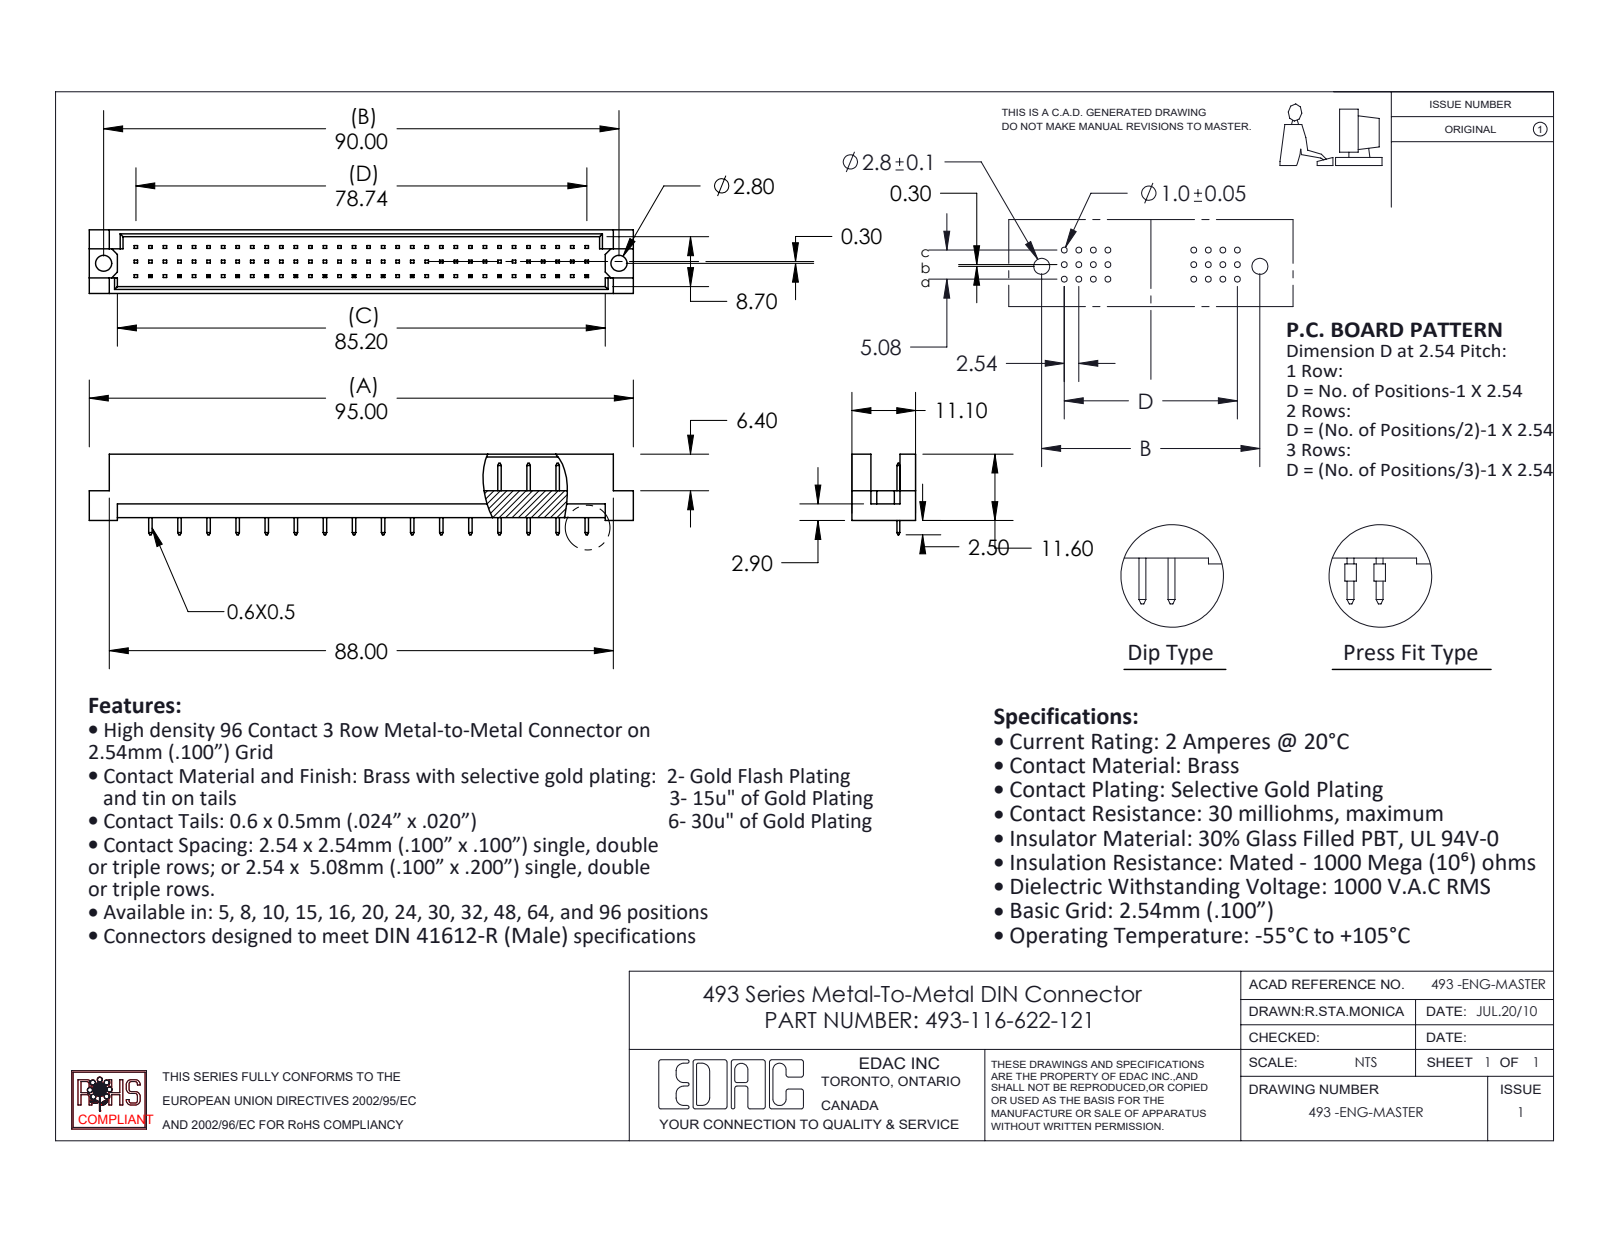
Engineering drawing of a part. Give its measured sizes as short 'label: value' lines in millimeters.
name: 493-116-622-122; 493-290_22; 493 Part_96
written by: SolidWorks 2020 (CONFIG_CONTROL_DESIGN)
unit: mm
bodies: 17 solids, 660 faces (656 planar, 4 cylindrical, 0 other)
size: 95 × 14.1 × 11.1
volume: 5 718 mm³; area: 6 909 mm²
holes: 2× ⌀2.8
face distances: 1.2, 9.9, 11.1, 8.7, 4.7, 0.5, 5.08, 2.54, 2.76, 8.34
hole spacings: 90
